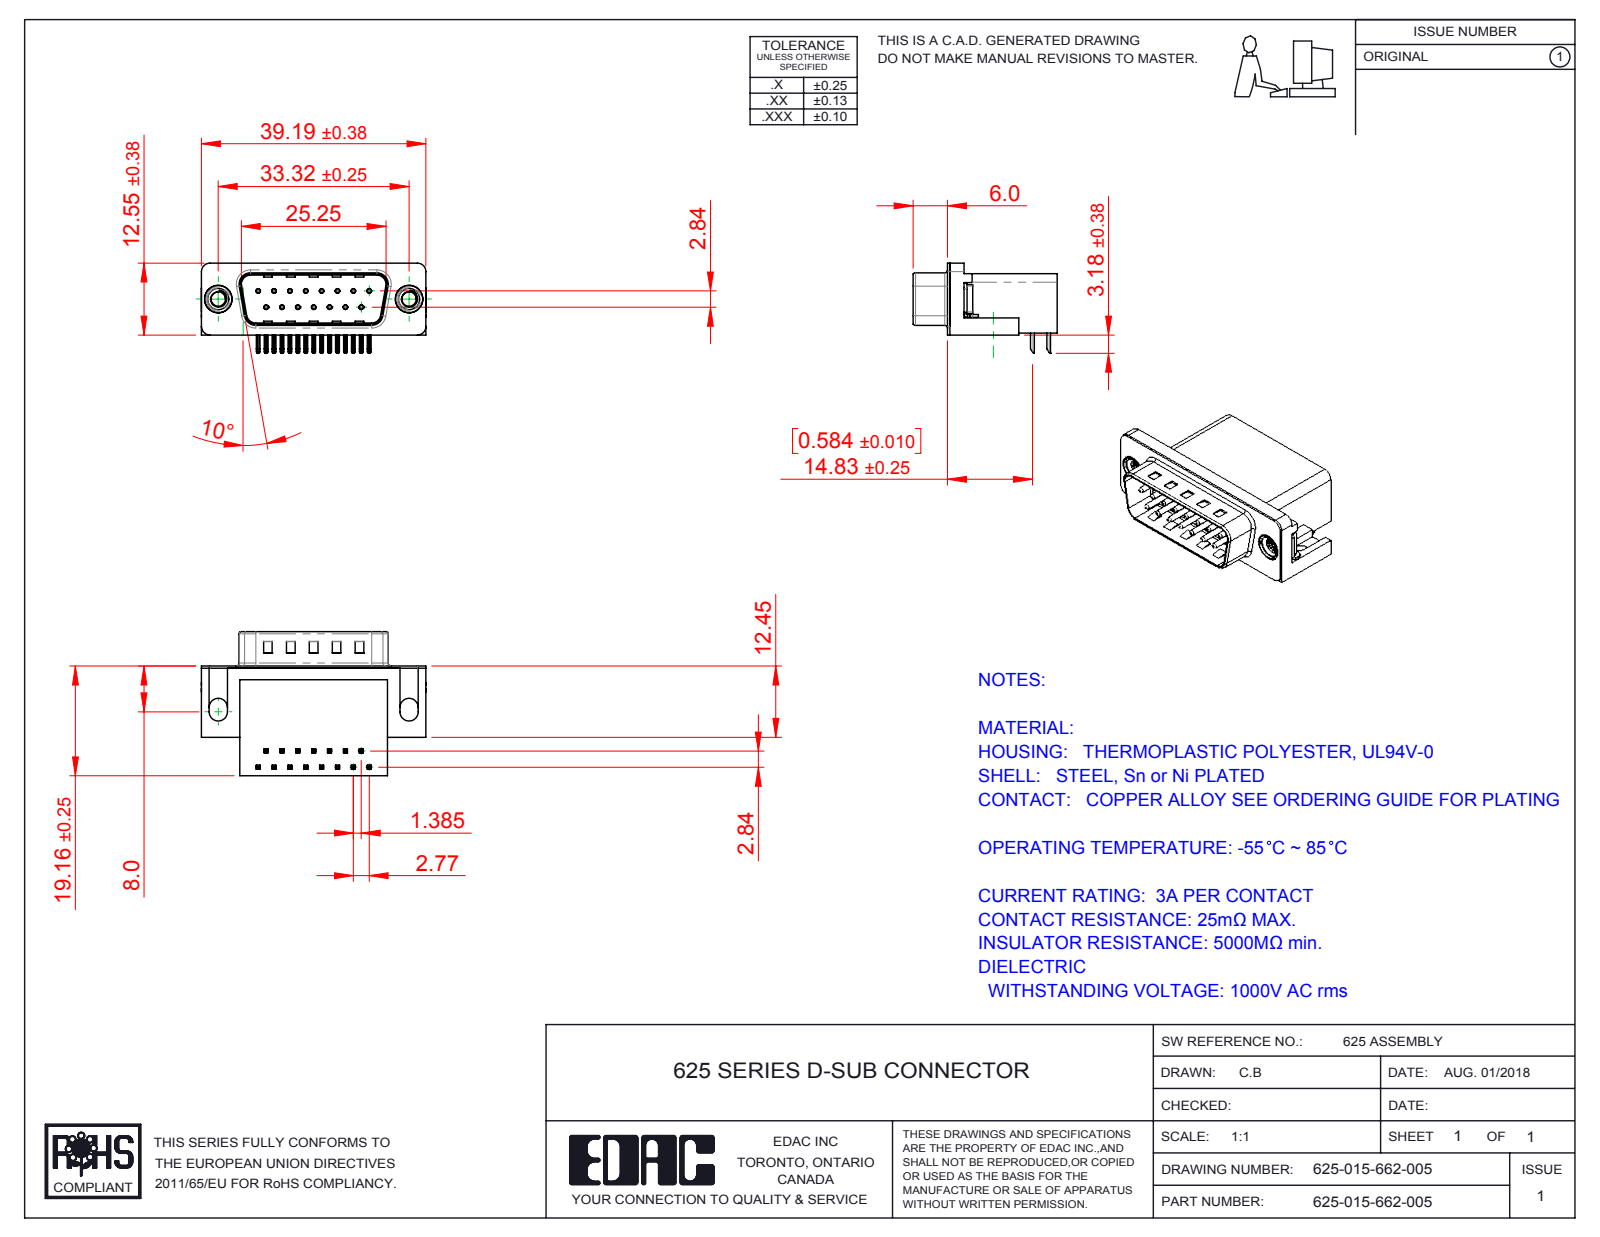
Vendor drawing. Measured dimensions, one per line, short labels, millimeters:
name: 625 Housing_15 Socket; 625 M3 Threaded Rivet; 625 Non Board Mount; 625 Contact Top (+3 more)
written by: SolidWorks 2016 (CONFIG_CONTROL_DESIGN)
unit: mm
bodies: 21 solids, 1477 faces (895 planar, 447 cylindrical, 135 other)
size: 39.22 × 25.16 × 15.73
volume: 6 210 mm³; area: 6 294 mm²
holes: 15× ⌀0.35, 15× ⌀0.8, 2× ⌀2.5, 2× ⌀4, 2× ⌀4.8, 2× ⌀5
bosses: 15× ⌀0.75, 2× ⌀4.9, 2× ⌀4.75, 2× ⌀3.9
rounds: 68× R0.25, 30× R0.12, 16× R1, 9× R0.5, 8× R1.6, 6× R1.5, 4× R0.9, 4× R2
face distances: 0.4, 10.35, 18.76, 2.1, 10.46, 19.16, 1.7, 10.86, 8.76, 16.26
hole spacings: 3.16, 2.77, 5.54, 8.31, 11.08, 5.03, 5.04, 7.48
